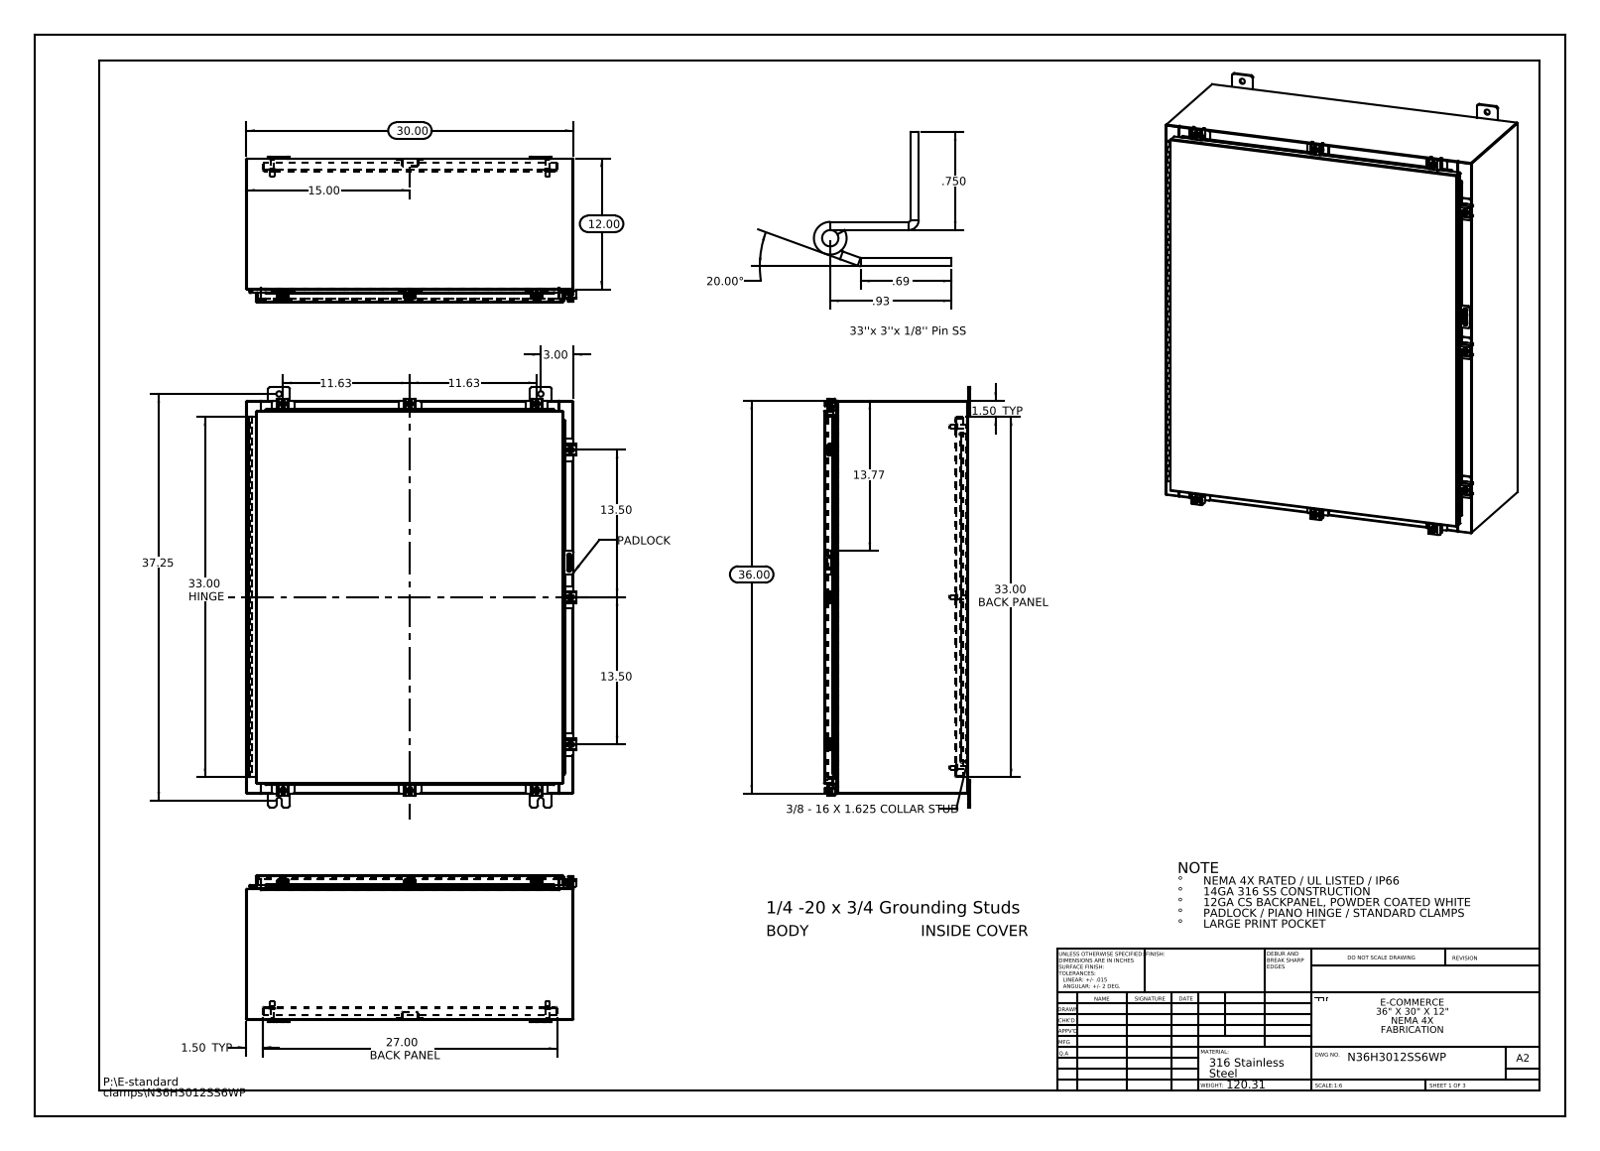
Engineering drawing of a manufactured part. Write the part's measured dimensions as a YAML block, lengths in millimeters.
part_name: "N36H3012SS6WP 22101002; N36H3012SS6WP Mounting Feet; N36H3012SS6WP Padlock Staple; N36H3012SS6WP Clamp Bracket (+8 more)"
step_written_by: "SolidWorks 2013 (CONFIG_CONTROL_DESIGN)"
units: millimeters
bodies: {solids: 65, faces: 2456, planar: 1288, cylindrical: 1028, other: 140}
overall_size: [977.9, 767.4, 340.1]
volume: 6910000
surface_area: 6821000
round_holes:
  - {diameter: 12.7, count: 10}
  - {diameter: 5.4, count: 9}
  - {diameter: 6.6, count: 9}
  - {diameter: 3.2, count: 2}
  - {diameter: 3.2, count: 1}
round_bosses_or_shafts:
  - {diameter: 6.4, count: 10}
  - {diameter: 12.7, count: 9}
  - {diameter: 10.1, count: 9}
  - {diameter: 15.9, count: 6}
  - {diameter: 9.5, count: 6}
  - {diameter: 8.4, count: 6}
partial_cylinders:
  - {radius: 1.5, count: 42}
  - {radius: 0.3, count: 31}
  - {radius: 2.2, count: 25}
  - {radius: 4.8, count: 24}
  - {radius: 3, count: 18}
  - {radius: 3.6, count: 18}
  - {radius: 1.3, count: 13}
  - {radius: 2, count: 12}
face_to_face_distances: [1.9, 333.4, 331.5, 335.3, 2.6, 25.4, 308, 27.3, 306.1, 29.9]
hole_center_spacings: [396.9, 451, 754.2, 847.5, 947.6, 641.4, 900.5, 47.2]
